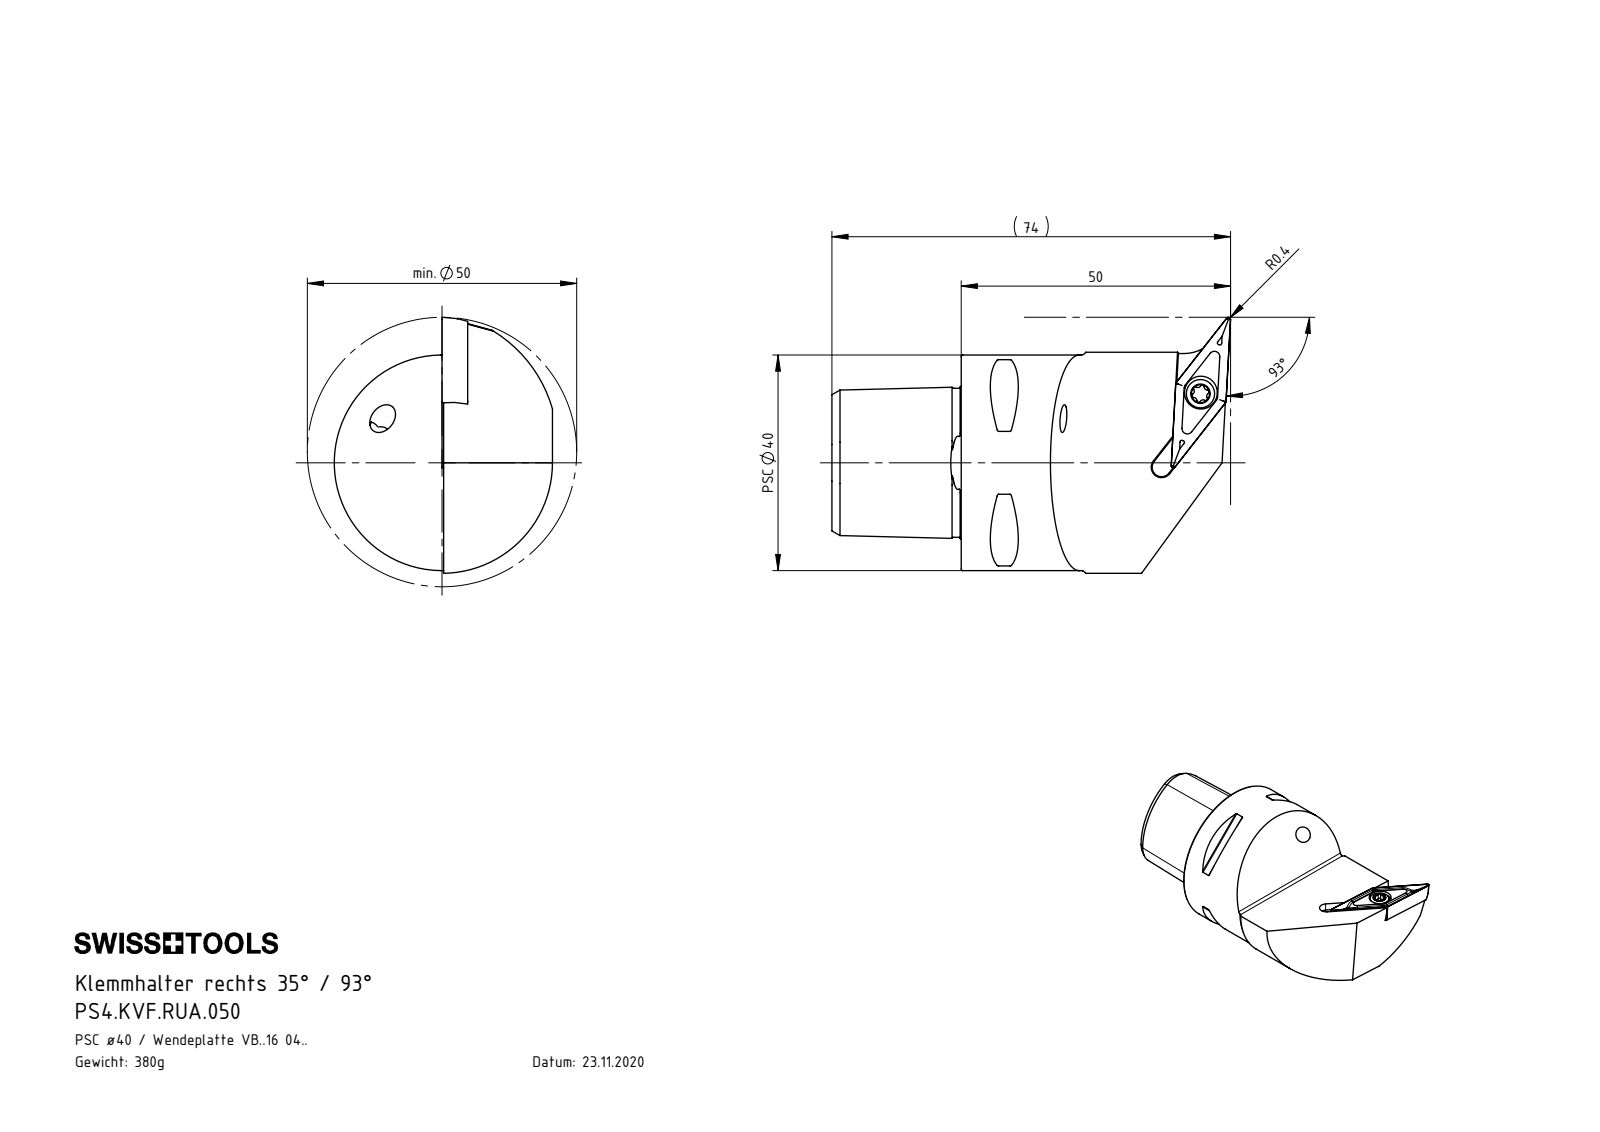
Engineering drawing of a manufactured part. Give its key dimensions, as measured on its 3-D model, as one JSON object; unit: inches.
{"part_name": "PS4.KVF.RUA.050; PS4-KVF.RUA.050_A; KVT_MB_600_050; WCB-ER2.001.009_A (+1 more)", "step_written_by": "SolidWorks 2017 (AUTOMOTIVE_DESIGN)", "units": "inches", "bodies": {"solids": 5, "faces": 210, "planar": 55, "cylindrical": 48, "other": 107}, "overall_size": [2.913, 1.87, 1.594], "volume_in3": 2.921, "surface_area_in2": 20.7, "round_holes": [[0.157, 2], [0.165, 2], [0.13, 1], [0.173, 1], [0.181, 1], [0.197, 1], [0.24, 1], [0.492, 1], [0.709, 1], [0.787, 1]], "round_bosses_or_shafts": [[1.575, 1], [0.207, 1], [0.197, 1], [0.157, 1]], "partial_cylinders_radius": [[0.012, 8], [0.013, 6], [0.023, 6], [0.006, 2], [0.031, 1], [0.069, 1], [0.118, 1], [0.276, 1]], "face_to_face_distances": [0.176, 0.62, 0.795, 0.945, 0.611, 1.39, 0.354, 0.591, 0.807, 0.187], "hole_center_spacings": [0.925, 1.372, 1.378, 2.258, 2.263]}
